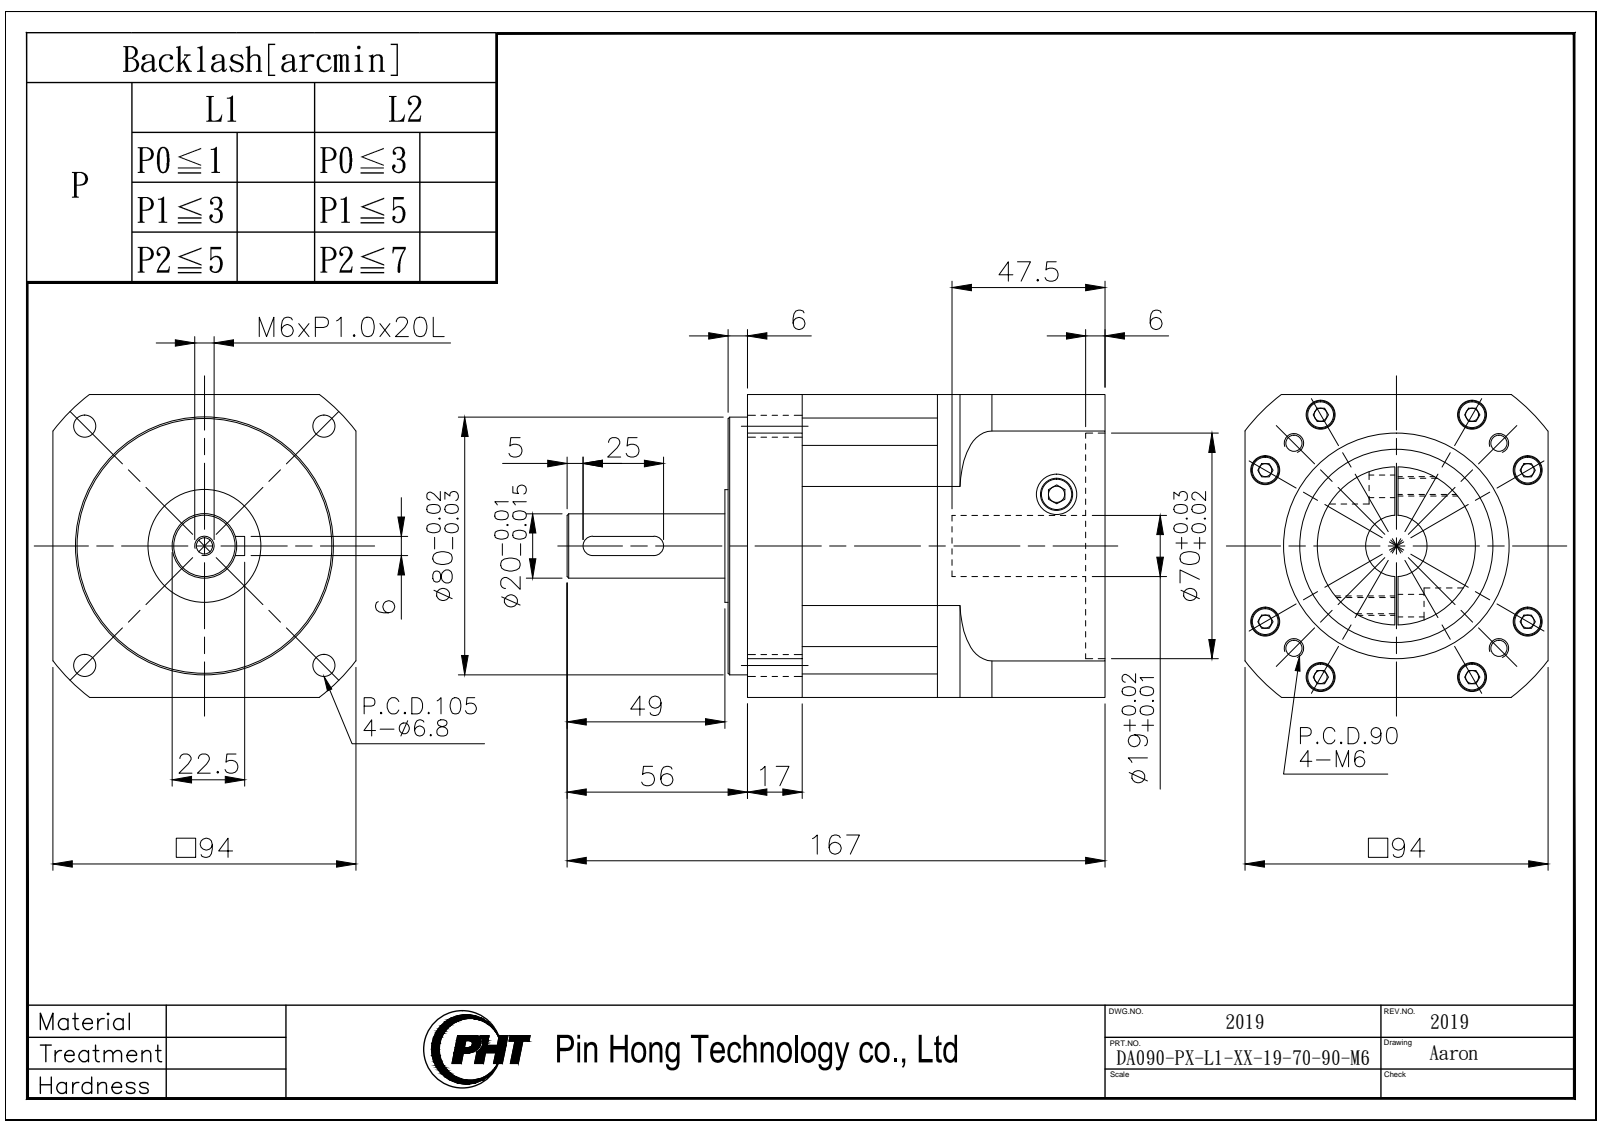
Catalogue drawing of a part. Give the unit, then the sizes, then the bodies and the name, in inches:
Units: inches
Overall size (bounding box): 6.575 × 3.701 × 3.701
Round holes (diameter × count): ⌀0.205 ×8, ⌀0.354 ×8, ⌀0.197 ×5, ⌀0.268 ×4, ⌀0.5 ×2, ⌀0.748 ×1, ⌀2.362 ×1, ⌀2.756 ×1
Round bosses / shafts (diameter × count): ⌀0.335 ×8, ⌀3.15 ×1, ⌀1.929 ×1, ⌀1.378 ×1, ⌀0.787 ×1
Partial cylindrical surfaces — rounded edges, fillets, slot ends (radius × count): R0.236 ×4, R0.118 ×2, R1.988 ×1, R2.323 ×1
Main face-to-face distances: 3.701, 1.654, 4.37, 0.236, 2.047, 4.606, 2.559, 0.906, 0.669, 1.811
Hole centre spacings: 1.85, 0.479, 0.554, 2.206, 2.391, 2.617, 2.722, 2.874
Volume: 51.17 in³ · Surface area: 195.5 in²
Bodies: 3 solids, 259 faces (112 planar, 115 cylindrical, 32 other)
Part name (STEP PRODUCT): DA090-PX-L1-XX-19-70-90-M6_2019
STEP written by: SolidWorks 2016 (AUTOMOTIVE_DESIGN)
